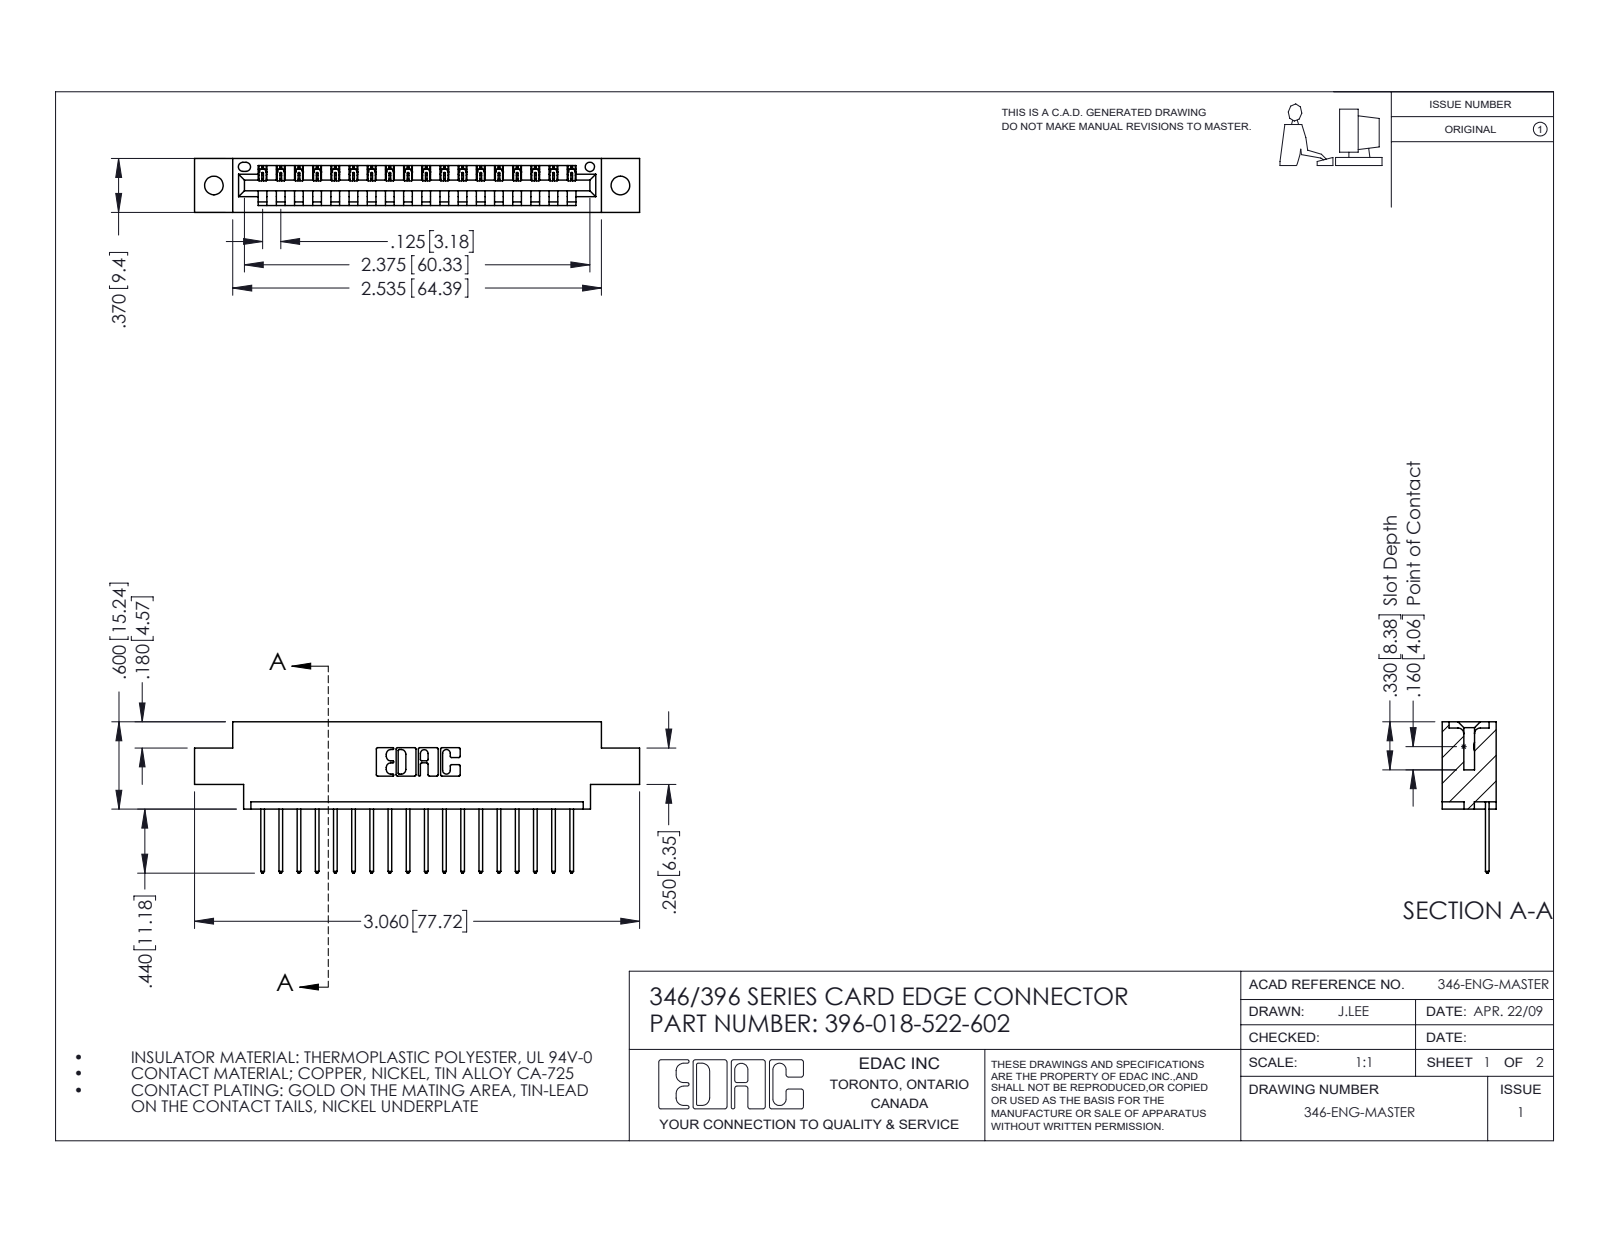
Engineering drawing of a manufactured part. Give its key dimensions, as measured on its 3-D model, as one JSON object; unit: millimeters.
{"part_name": "396-018-522-602; 345-292-001_345-293-122; 346 Part_0.170 Offset - 0.128 Dia", "step_written_by": "SolidWorks 2016 (CONFIG_CONTROL_DESIGN)", "units": "millimeters", "bodies": {"solids": 19, "faces": 1170, "planar": 800, "cylindrical": 370, "other": 0}, "overall_size": [77.7, 26.4, 9.4], "volume_mm3": 7080, "surface_area_mm2": 8555, "round_holes": [[3.3, 2], [1.6, 1]], "partial_cylinders_radius": [[0.2, 36], [0.3, 36], [0.3, 22], [0.2, 6], [0.8, 6], [0.7, 3], [0.8, 2], [1, 2]], "face_to_face_distances": [1.2, 8.2, 9.4, 6.4, 1.8, 7.6, 0.6, 3.8, 5.6, 2.5], "hole_center_spacings": [6.2, 65.7, 71]}
